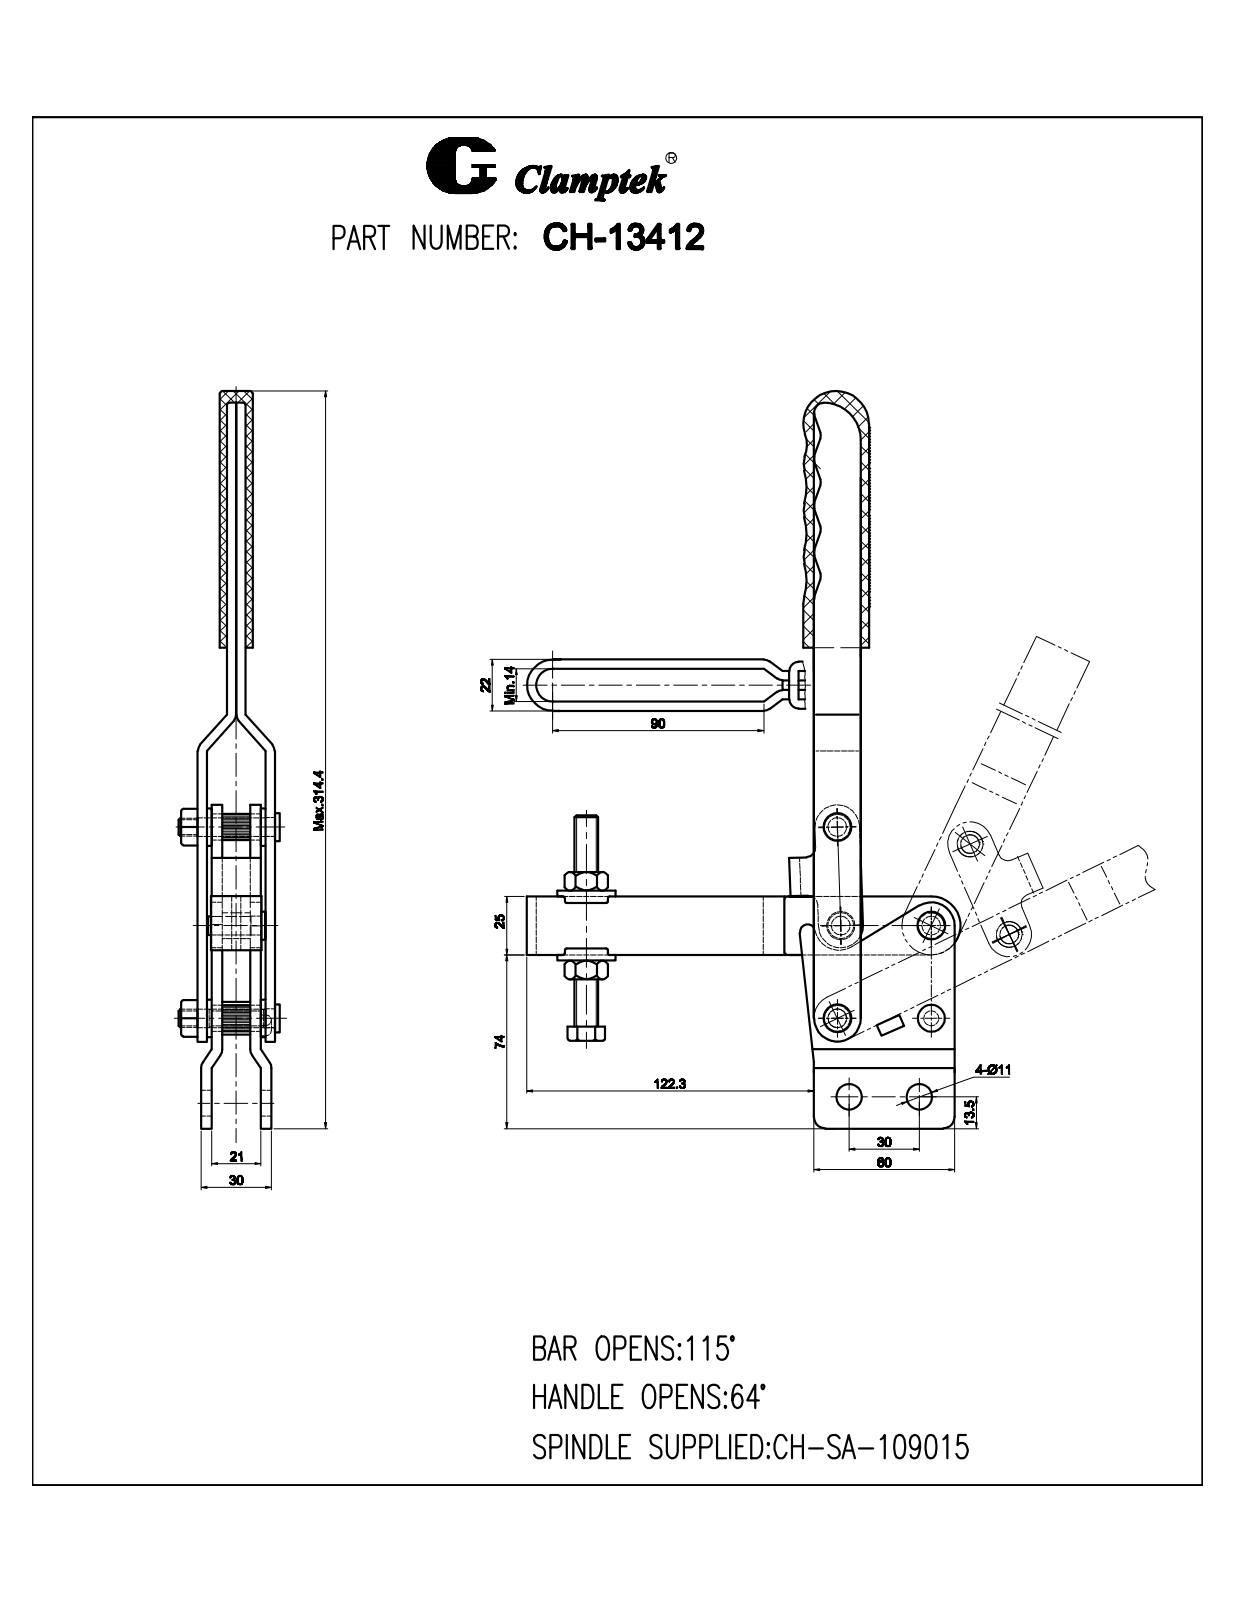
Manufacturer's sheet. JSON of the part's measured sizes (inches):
{"part_name": "CH-13412-01 STRAIGHT BASE; CH-14412-10; CH-14412-07; CH-FW-120 (+8 more)", "step_written_by": "SolidWorks 2010 (CONFIG_CONTROL_DESIGN)", "units": "inches", "bodies": {"solids": 30, "faces": 1790, "planar": 681, "cylindrical": 602, "other": 507}, "overall_size": [12.45, 7.392, 1.693], "volume_in3": 13.15, "surface_area_in2": 203.4, "round_holes": [[0.433, 6], [0.315, 4], [0.268, 2], [0.157, 1], [0.18, 1], [0.252, 1], [0.335, 1], [0.512, 1]], "round_bosses_or_shafts": [[0.472, 4], [0.63, 2], [0.551, 1], [0.394, 1], [0.315, 1], [0.126, 1]], "partial_cylinders_radius": [[0.01, 84], [0.157, 15], [1.02, 8], [0.138, 7], [0.177, 6], [0.394, 6], [0.118, 4], [0.197, 3]], "face_to_face_distances": [0.079, 0.157, 0.65, 0.571, 0.492, 0.236, 0.413, 0.256, 0.177, 0.335], "hole_center_spacings": [1.326, 1.902, 1.181, 1.543, 1.555, 1.556, 1.575, 1.654]}
